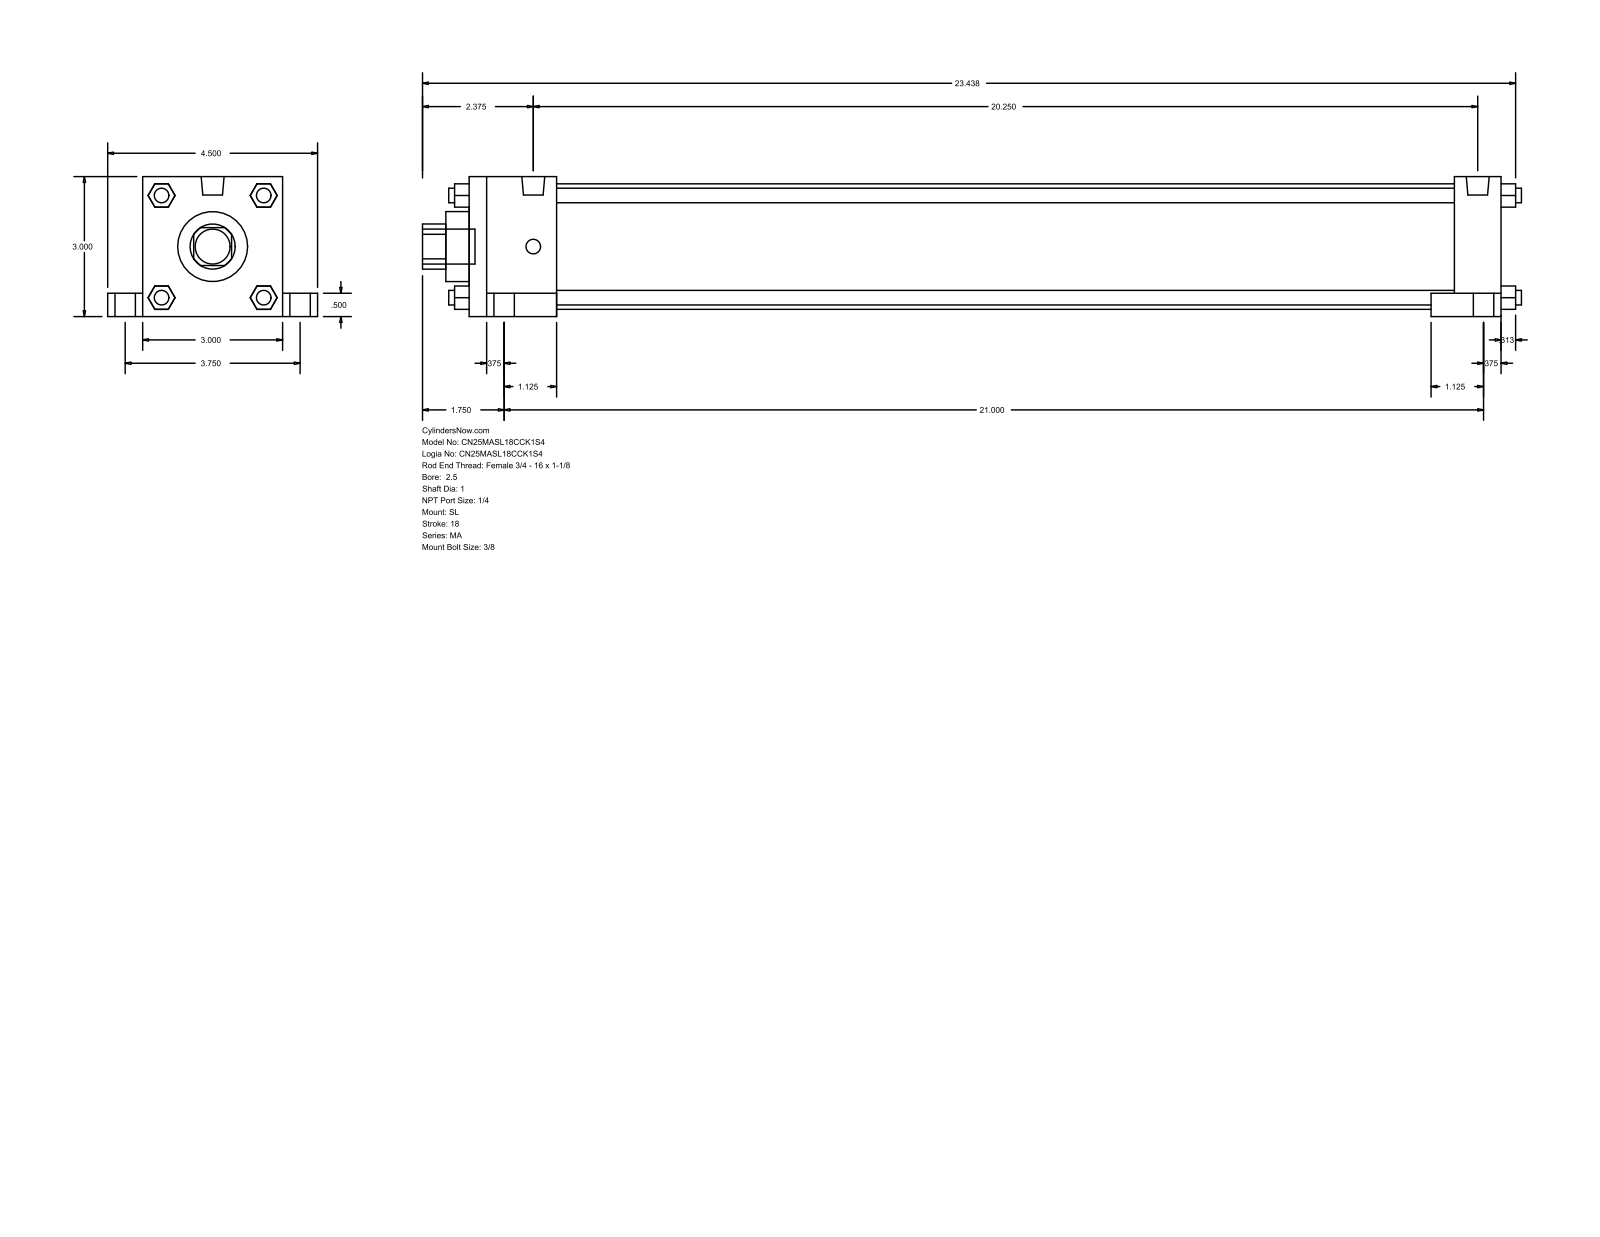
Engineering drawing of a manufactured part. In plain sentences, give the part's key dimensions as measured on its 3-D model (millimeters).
The part is named "MA_SL__0250_1". Its 3-D file was written by "GSSL Pune (CONFIG_CONTROL_DESIGN)". It is 0 solids with 148 faces: 112 planar, 36 cylindrical and 0 other. Overall it measures 598.49 by 114.3 by 76.2 millimeters. Round holes: 1 of diameter 25.4, 1 of diameter 38.1, 1 of diameter 68.33. Round bosses or shafts: 8 of diameter 7.94, 4 of diameter 17.46, 4 of diameter 11.11, 2 of diameter 12.49, 1 of diameter 19.05. Partial cylindrical surfaces (rounded edges, fillets, slot ends): 1 of radius 12.29. The main face-to-face distances are 76.2, 561.98, 12.7, 488.95, 25.4, 47.63, 514.35, 536.58, 19.05, 95.25.
